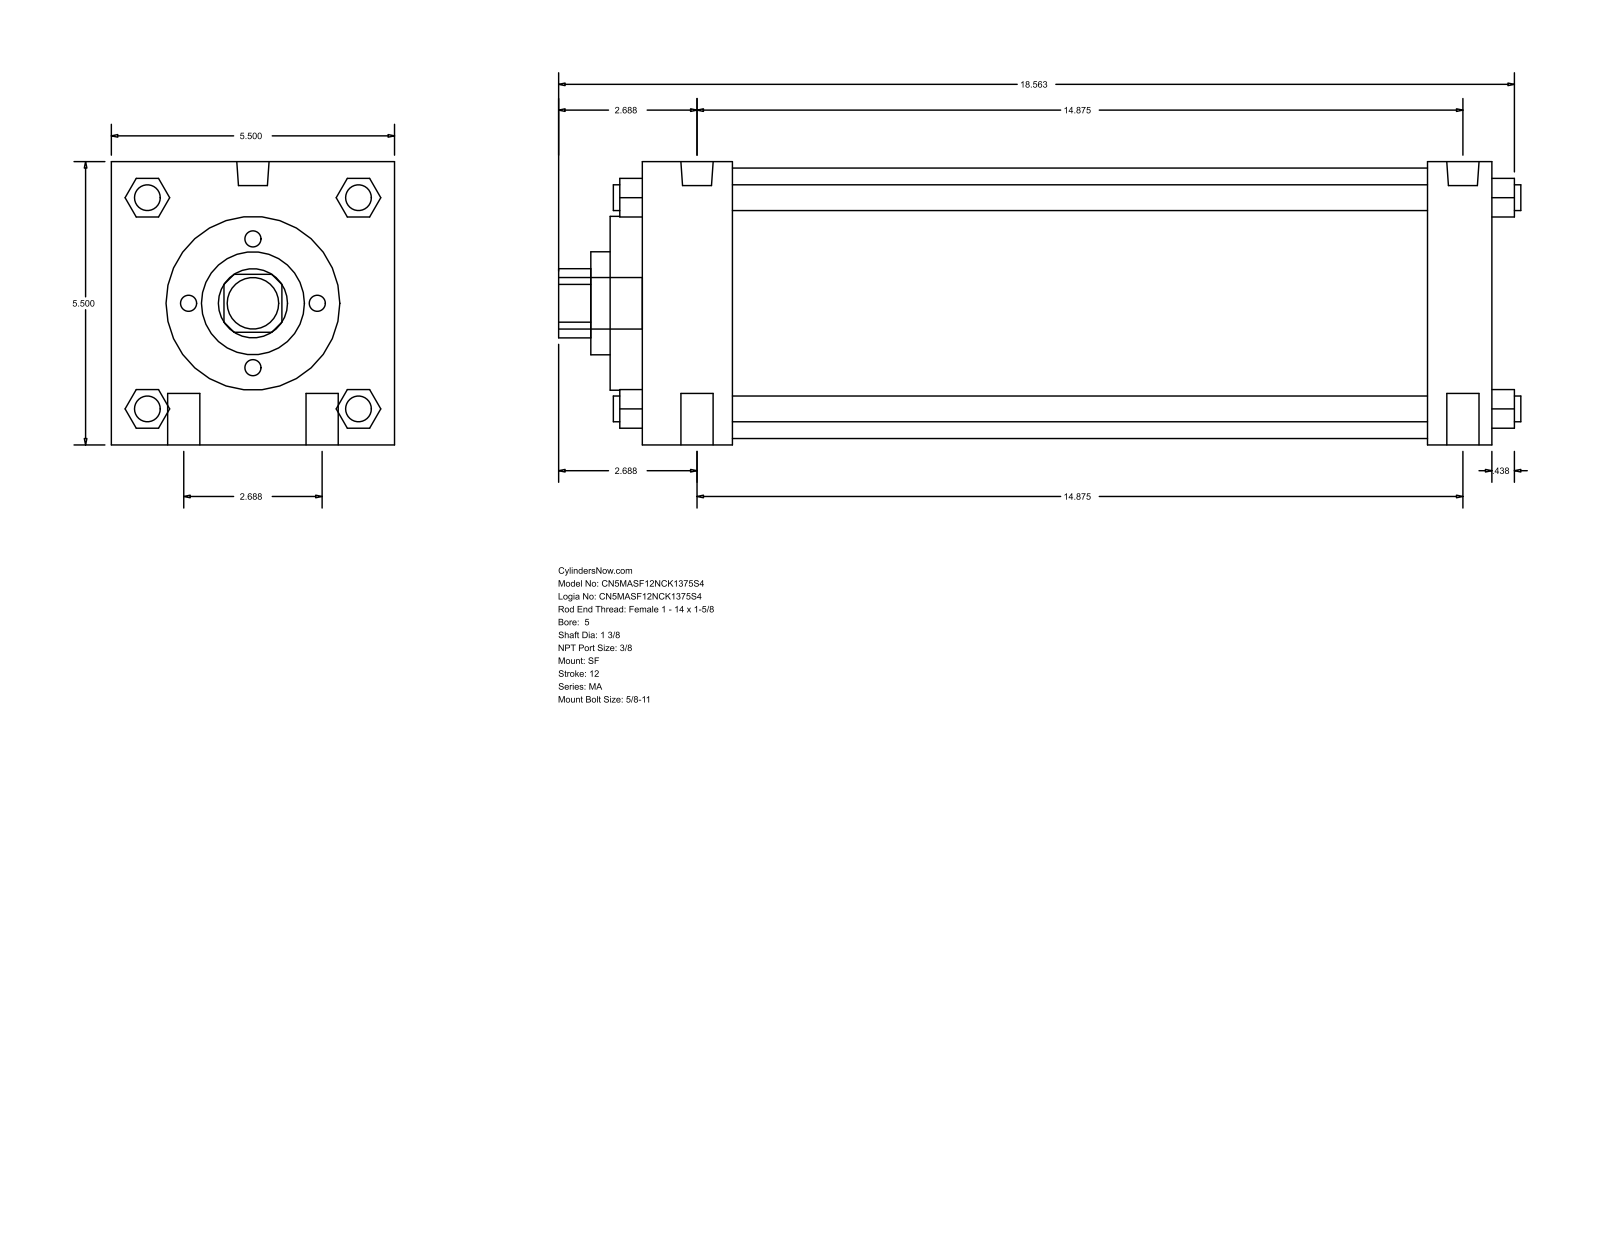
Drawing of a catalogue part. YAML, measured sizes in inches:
part_name: "MA_SF__0500_1.375"
step_written_by: "GSSL Pune (CONFIG_CONTROL_DESIGN)"
units: inches
bodies: {solids: 0, faces: 126, planar: 95, cylindrical: 31, other: 0}
overall_size: [18.687, 5.5, 5.5]
round_holes:
  - {diameter: 1.375, count: 1}
  - {diameter: 2, count: 1}
  - {diameter: 3.375, count: 1}
  - {diameter: 5.25, count: 1}
round_bosses_or_shafts:
  - {diameter: 0.625, count: 4}
  - {diameter: 0.5, count: 4}
  - {diameter: 0.627, count: 2}
  - {diameter: 0.437, count: 2}
  - {diameter: 1, count: 1}
partial_cylinders:
  - {radius: 0.672, count: 1}
face_to_face_distances: [5.5, 16.5, 1.75, 15.25, 13.5, 14.75, 1.25, 0.625, 2.375, 15.875]
